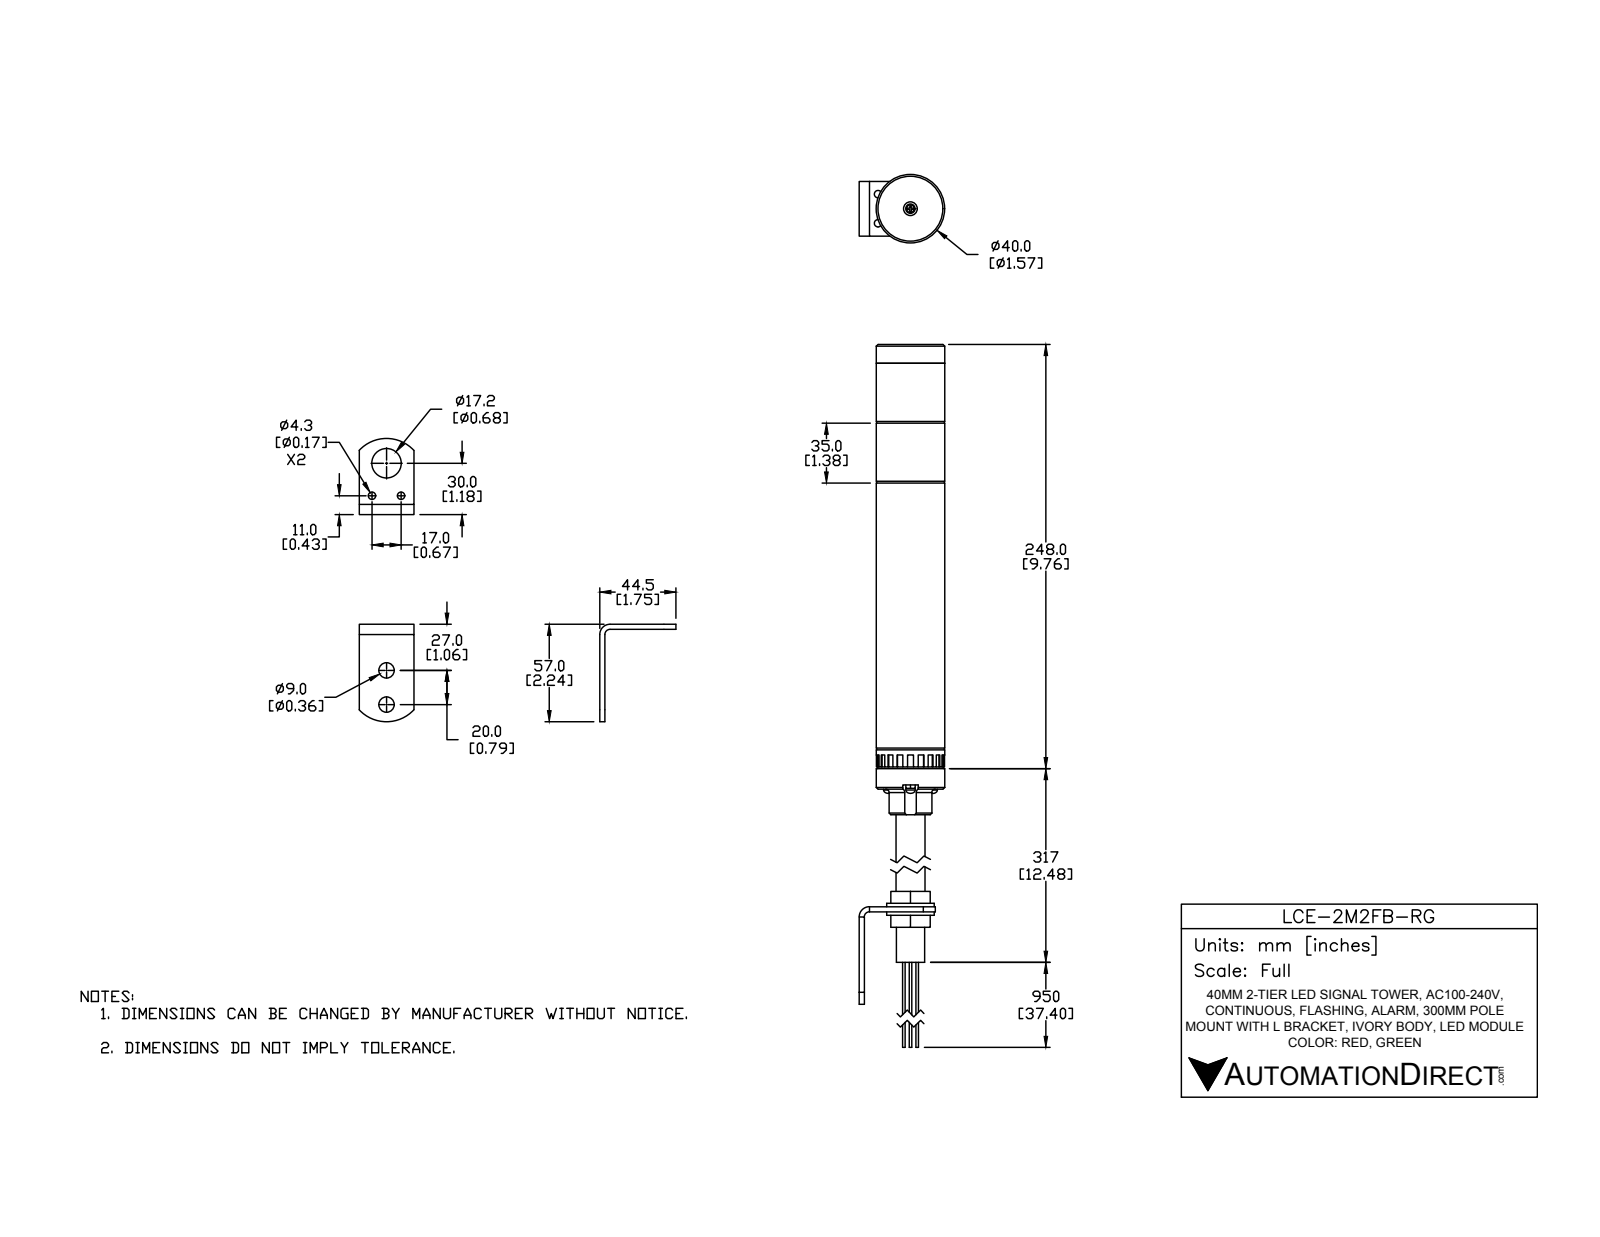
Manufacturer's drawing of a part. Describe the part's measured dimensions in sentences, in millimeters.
The part is named "LCE-2M2FB-RG". Its 3-D file was written by "SolidWorks 2016 (AUTOMOTIVE_DESIGN)". It is 36 solids with 389 faces: 247 planar, 122 cylindrical and 20 other. Overall it measures 666 by 50 by 40 millimeters. Its volume is 388 567 cubic millimeters and its surface area 131 901 square millimeters. Round holes: 3 of diameter 3.5, 3 of diameter 4, 2 of diameter 4.3, 2 of diameter 9.04, 1 of diameter 8, 1 of diameter 12, 1 of diameter 17.2, 1 of diameter 17.5, 1 of diameter 18. Round bosses or shafts: 10 of diameter 1.5, 6 of diameter 3, 4 of diameter 5.5, 1 of diameter 40, 1 of diameter 39.5, 1 of diameter 38.5, 1 of diameter 27.8, 1 of diameter 17. Partial cylindrical surfaces (rounded edges, fillets, slot ends): 3 of radius 4.5, 2 of radius 21.79, 1 of radius 3, 1 of radius 6, 1 of radius 12.5. The main face-to-face distances are 1, 35, 11, 34, 156, 191, 167, 202, 237, 236. The hole center spacings are 15, 25.98, 20.81, 6.09, 17, 17.09, 20, 20.08.
